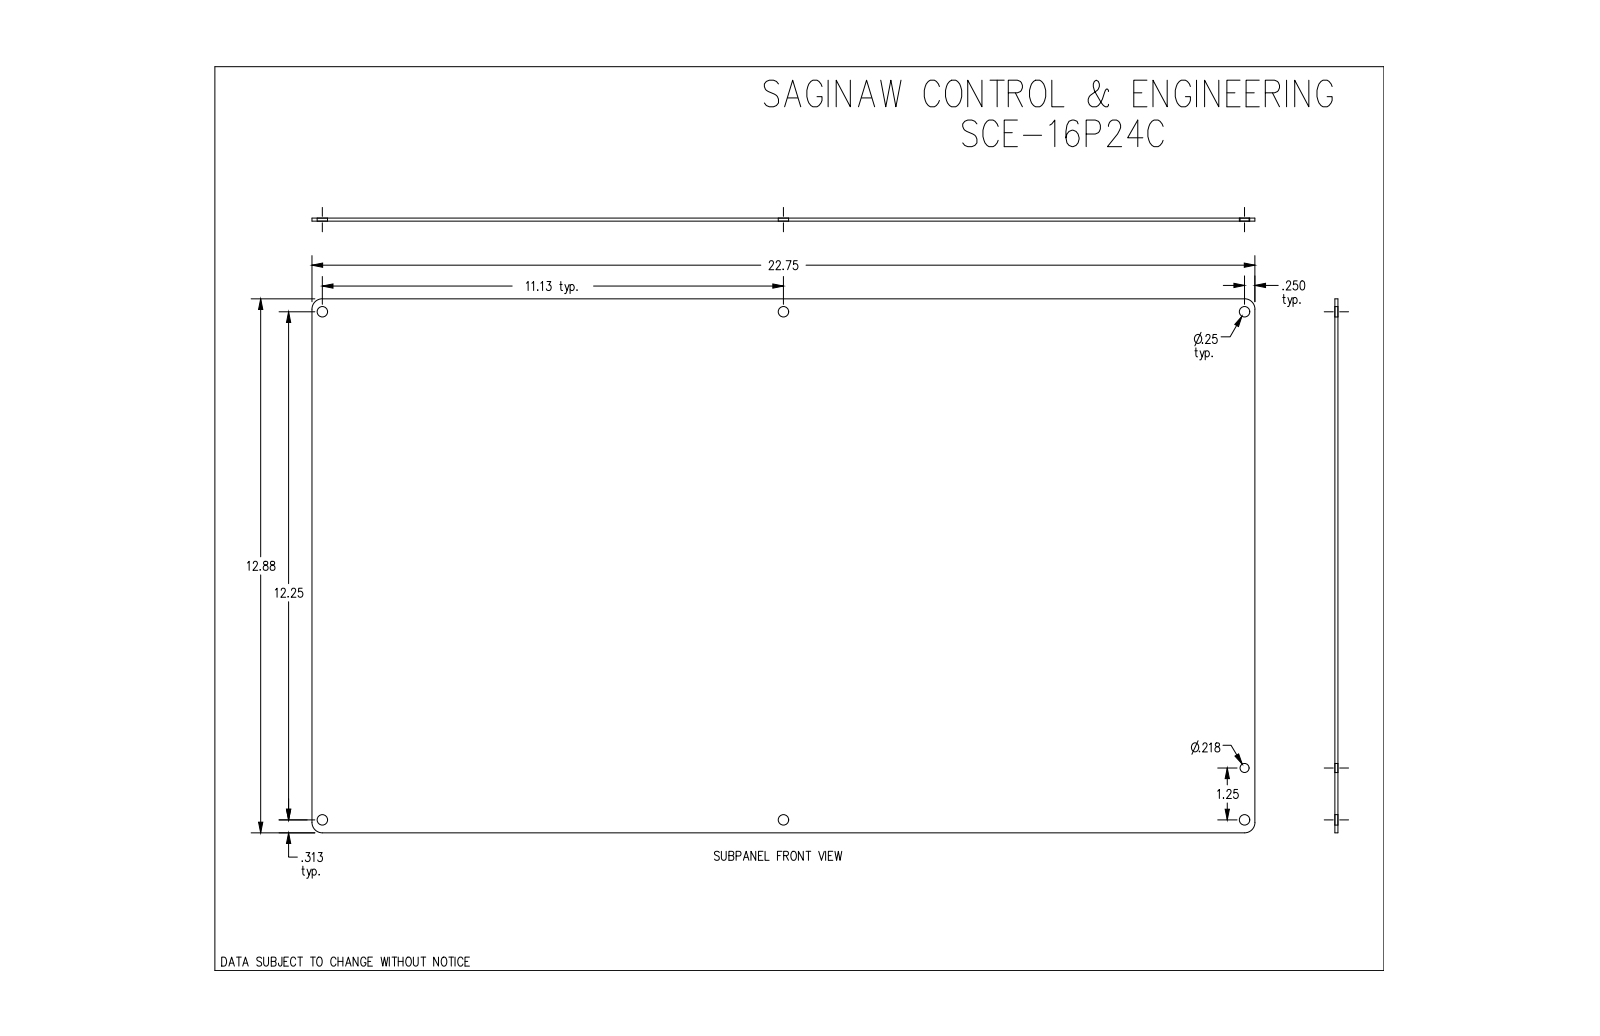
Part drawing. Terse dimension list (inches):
name: SCE-16P24C
written by: SolidWorks 2019 (CONFIG_CONTROL_DESIGN)
unit: in
bodies: 1 solid, 17 faces (6 planar, 11 cylindrical, 0 other)
size: 22.75 × 12.875 × 0.075
volume: 21.94 in³; area: 590.8 in²
holes: 6× ⌀0.25, 1× ⌀0.218
rounds: 4× R0.25
face distances: 0.075, 12.875, 22.75
hole spacings: 11.125, 16.547, 12.25, 22.25, 25.399, 1.25, 11, 11.195
